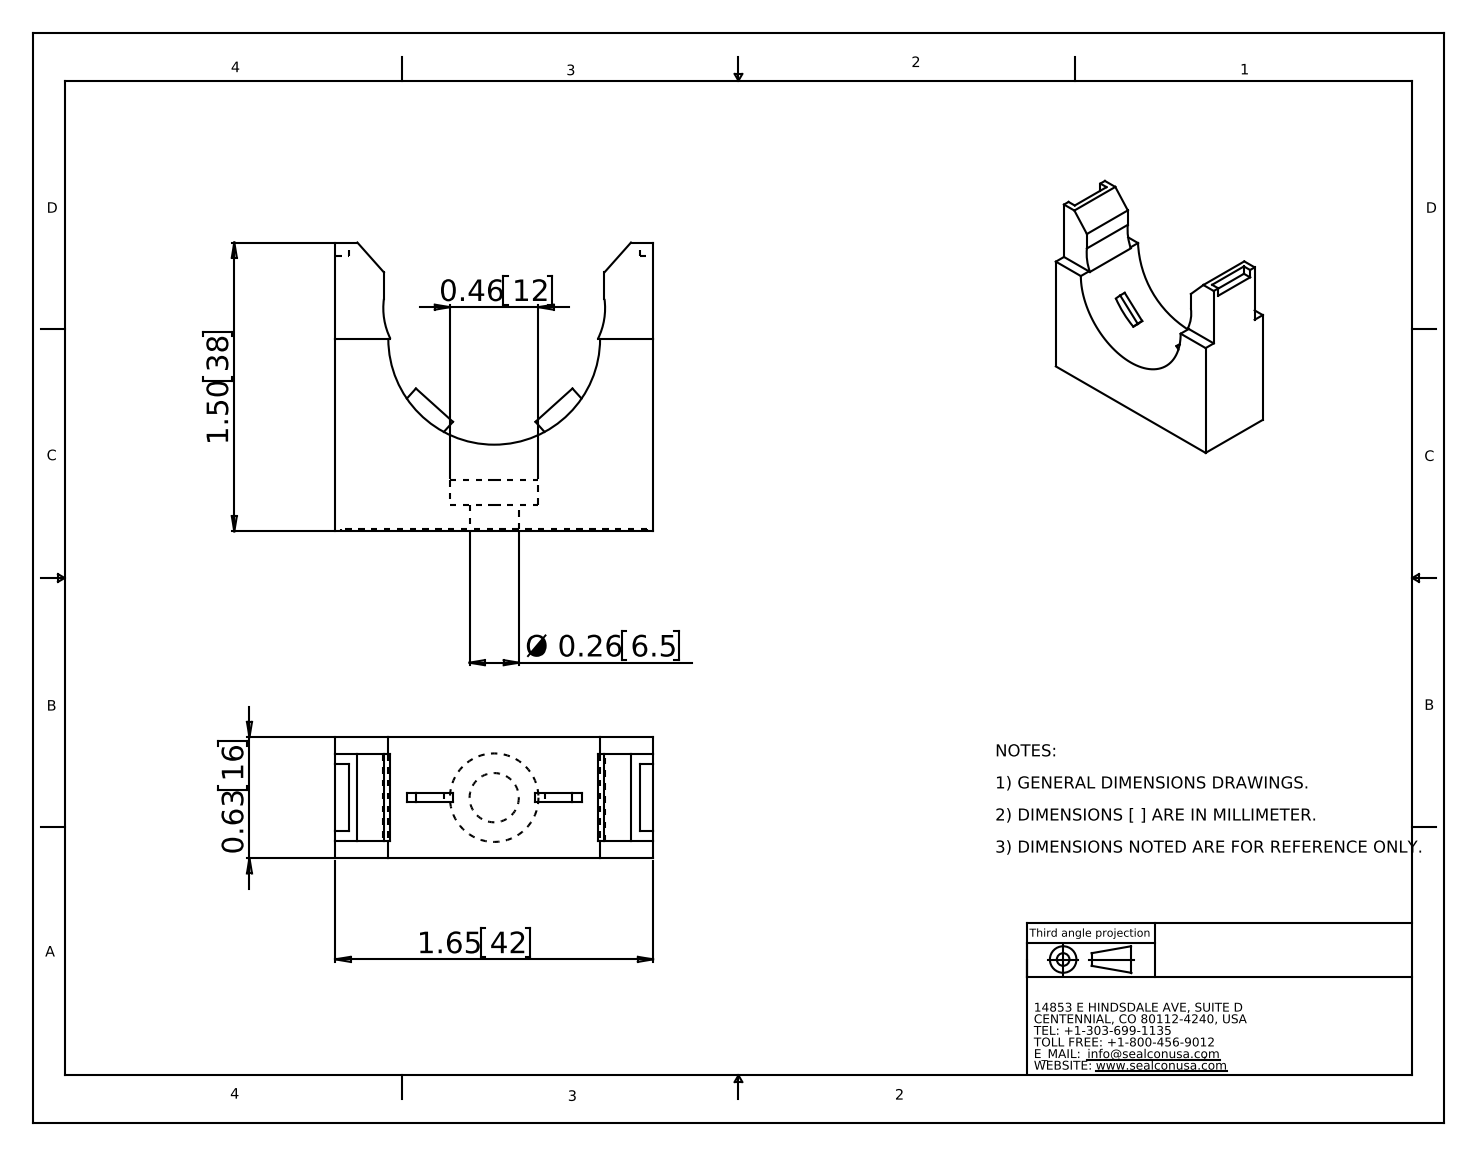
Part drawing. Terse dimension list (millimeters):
name: MB-21-BK
written by: SolidWorks 2008 (CONFIG_CONTROL_DESIGN)
unit: mm
bodies: 1 solid, 54 faces (46 planar, 8 cylindrical, 0 other)
size: 41.9 × 38.1 × 16
volume: 13 200 mm³; area: 5 192 mm²
holes: 1× ⌀6.5, 1× ⌀11.7
rounds: 2× R9.1, 1× R14
face distances: 16, 41.9, 2.3, 13.7, 11.5, 3.3, 6.5, 6.8, 3.5, 25.4
